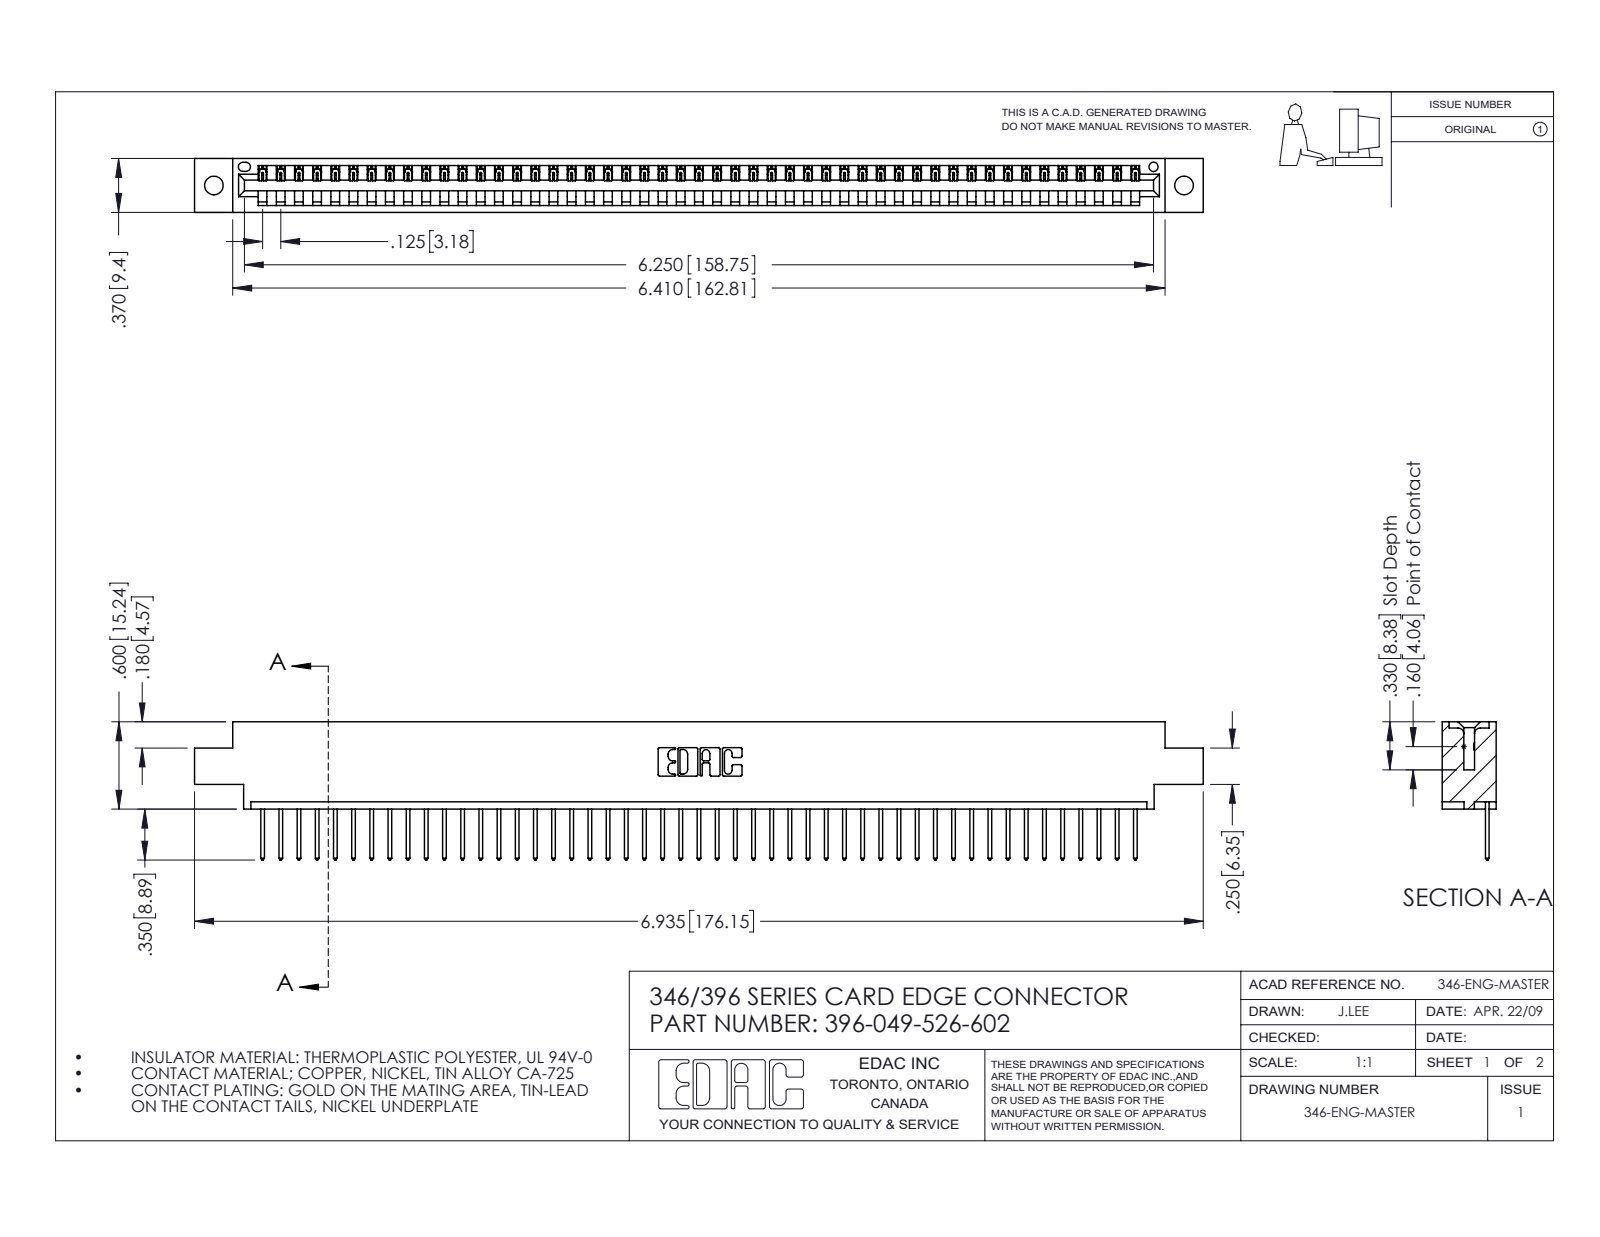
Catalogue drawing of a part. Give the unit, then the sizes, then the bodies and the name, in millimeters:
Units: millimetres
Overall size (bounding box): 176.1 × 24.1 × 9.4
Round holes (diameter × count): ⌀3.3 ×2, ⌀1.6 ×1
Partial cylindrical surfaces — rounded edges, fillets, slot ends (radius × count): R0.2 ×98, R0.3 ×98, R0.3 ×22, R0.2 ×6, R0.8 ×6, R0.7 ×3, R0.8 ×2, R1 ×2
Main face-to-face distances: 1.2, 8.2, 9.4, 6.4, 1.8, 7.6, 0.6, 3.8, 5.6, 2.5
Hole centre spacings: 6.2, 164.1, 169.4
Volume: 16 680 mm³ · Surface area: 20 760 mm²
Bodies: 50 solids, 2968 faces (2040 planar, 928 cylindrical, 0 other)
Part name (STEP PRODUCT): 346 Part_0.170 Offset - 0.128 Dia; 396-049-526-602; 345-292-001_345-293-126
STEP written by: SolidWorks 2016 (CONFIG_CONTROL_DESIGN)
